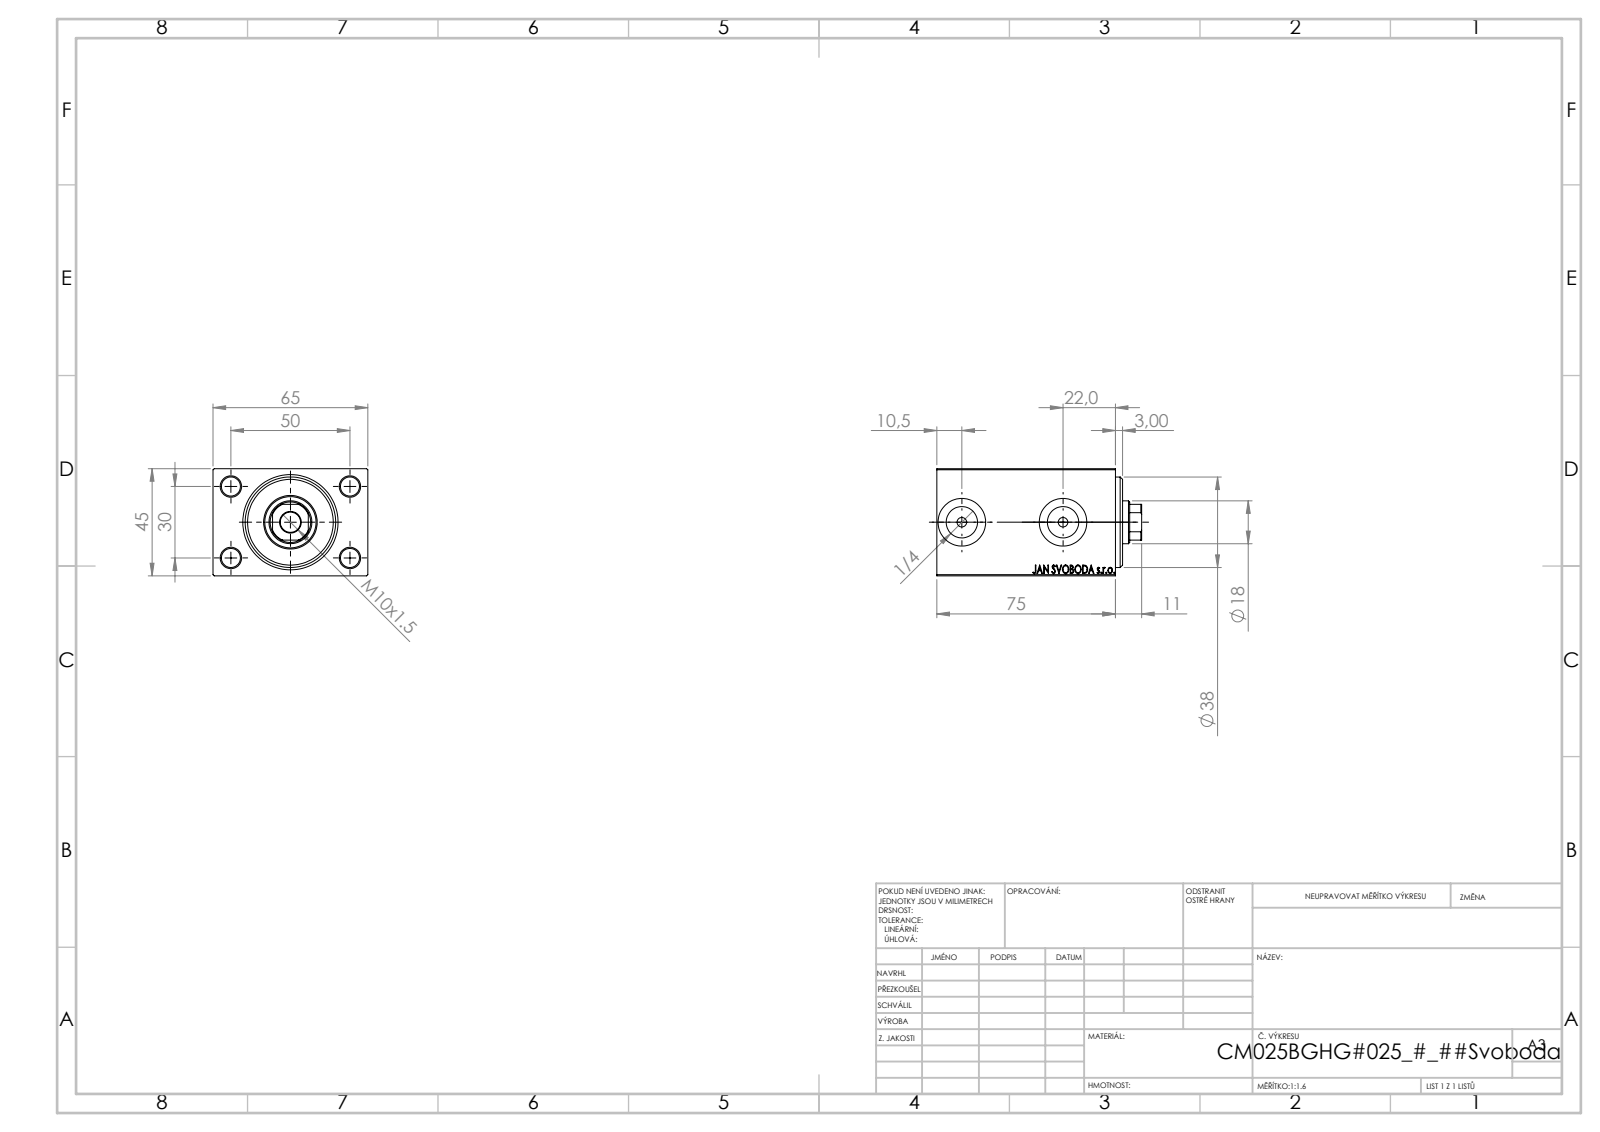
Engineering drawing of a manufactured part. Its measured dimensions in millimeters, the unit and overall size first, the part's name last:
Units: millimetres
Overall size (bounding box): 86 × 65 × 45
Round holes (diameter × count): ⌀8 ×4, ⌀4 ×2, ⌀13.16 ×2, ⌀20 ×2, ⌀8.5 ×1, ⌀18 ×1, ⌀21.5 ×1, ⌀22.5 ×1, ⌀25 ×1, ⌀27 ×1, ⌀38 ×1
Partial cylindrical surfaces — rounded edges, fillets, slot ends (radius × count): R8.5 ×1
Main face-to-face distances: 45, 65, 75, 6, 64, 5, 70, 69, 8, 3
Hole centre spacings: 29.15, 30, 50, 58.31, 42.5
Volume: 207 261 mm³ · Surface area: 42 794 mm²
Bodies: 3 solids, 881 faces (401 planar, 54 cylindrical, 426 other)
Part name (STEP PRODUCT): V450CM_B_Body; V450CM_B_VCP; V450CM_VC_B
STEP written by: SolidWorks 2019 (CONFIG_CONTROL_DESIGN)
